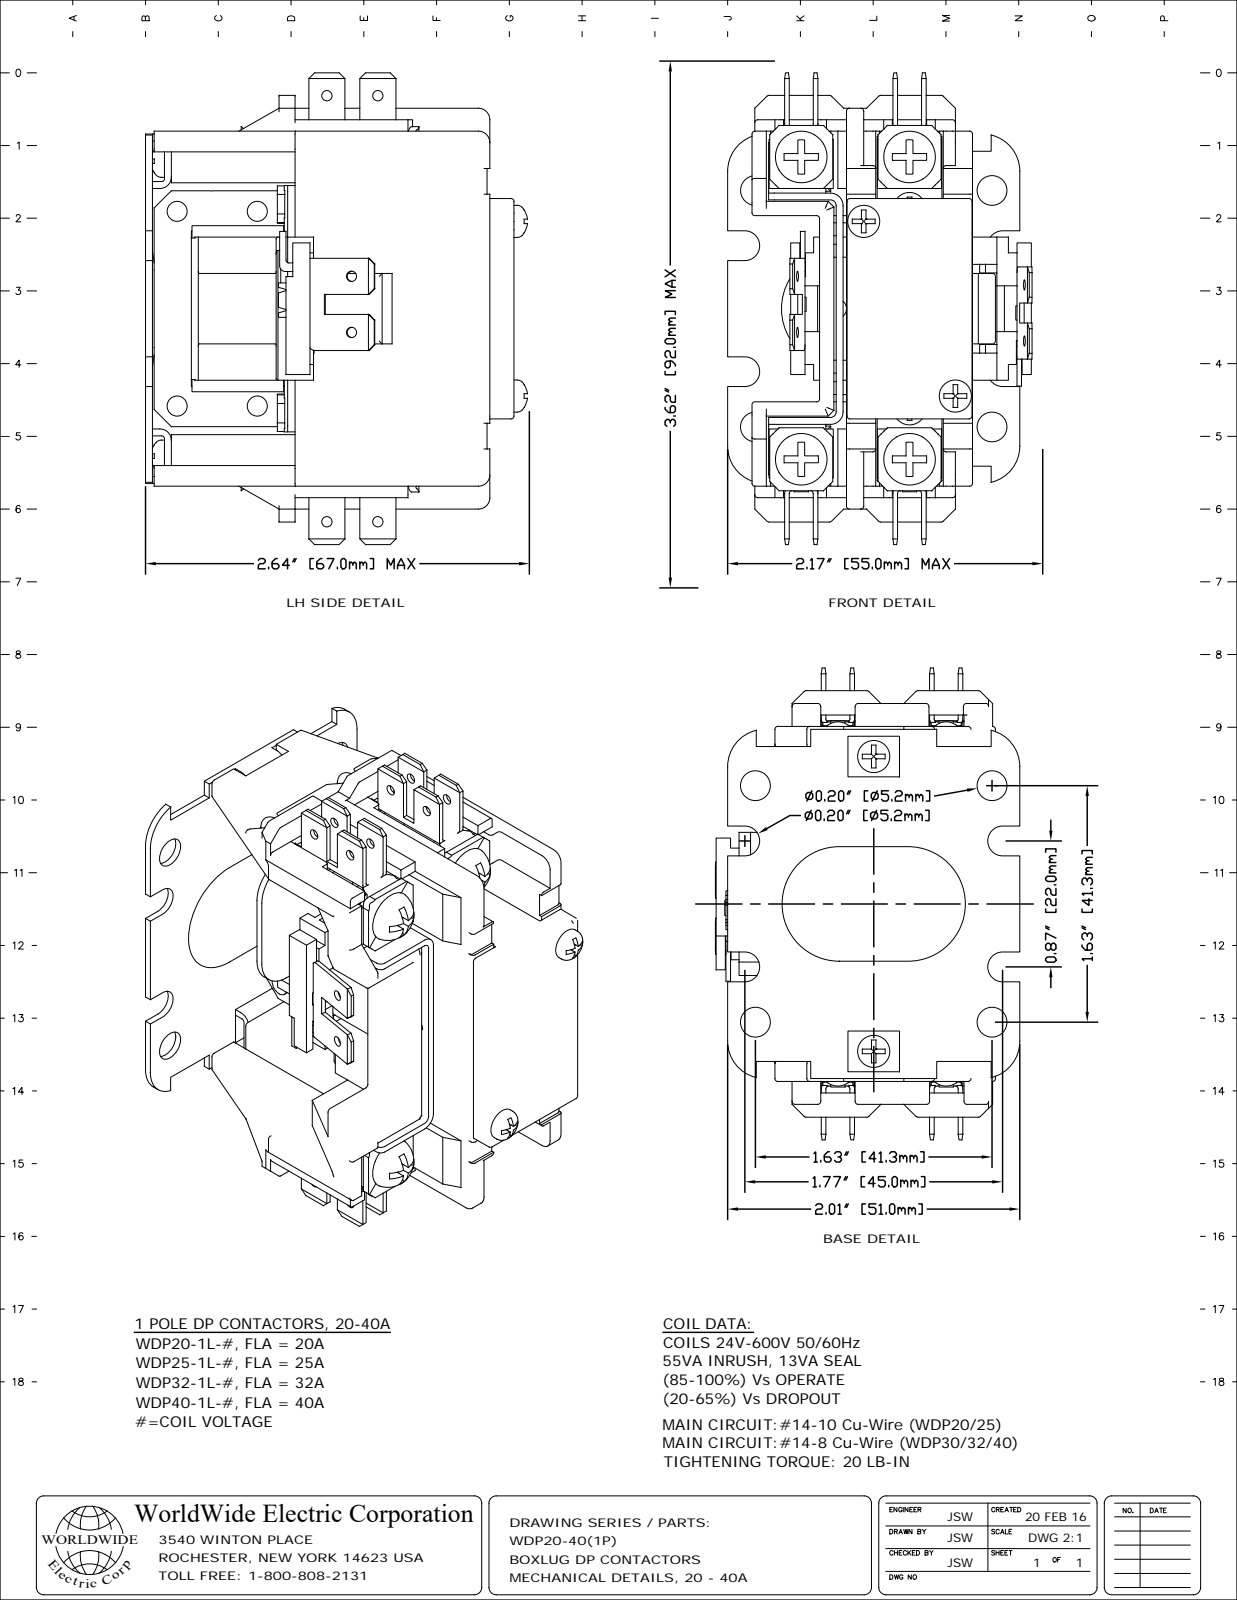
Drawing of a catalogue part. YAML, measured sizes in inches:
part_name: "WDP40-1L-230"
step_written_by: "SolidWorks 2017 (AUTOMOTIVE_DESIGN)"
units: inches
bodies: {solids: 8, faces: 2513, planar: 1645, cylindrical: 624, other: 244}
overall_size: [3.244, 2.624, 2.092]
volume: 4.03
surface_area: 86.02
round_holes:
  - {diameter: 0.071, count: 8}
  - {diameter: 0.098, count: 6}
  - {diameter: 0.118, count: 6}
  - {diameter: 0.205, count: 6}
  - {diameter: 0.217, count: 4}
round_bosses_or_shafts:
  - {diameter: 0.138, count: 13}
  - {diameter: 0.22, count: 6}
  - {diameter: 0.197, count: 4}
  - {diameter: 0.256, count: 2}
  - {diameter: 0.236, count: 2}
  - {diameter: 0.161, count: 2}
  - {diameter: 0.157, count: 2}
partial_cylinders:
  - {radius: 0.02, count: 150}
  - {radius: 0.039, count: 44}
  - {radius: 0.012, count: 28}
  - {radius: 0.031, count: 20}
  - {radius: 0.079, count: 12}
  - {radius: 0.051, count: 10}
  - {radius: 0.046, count: 8}
  - {radius: 0.059, count: 6}
face_to_face_distances: [0.047, 0.315, 0.295, 0.197, 0.079, 0.354, 0.492, 0.748, 0.689, 0.866]
hole_center_spacings: [0.327, 0.837, 1.327, 1.626, 2, 0.33, 0.35, 0.386]
